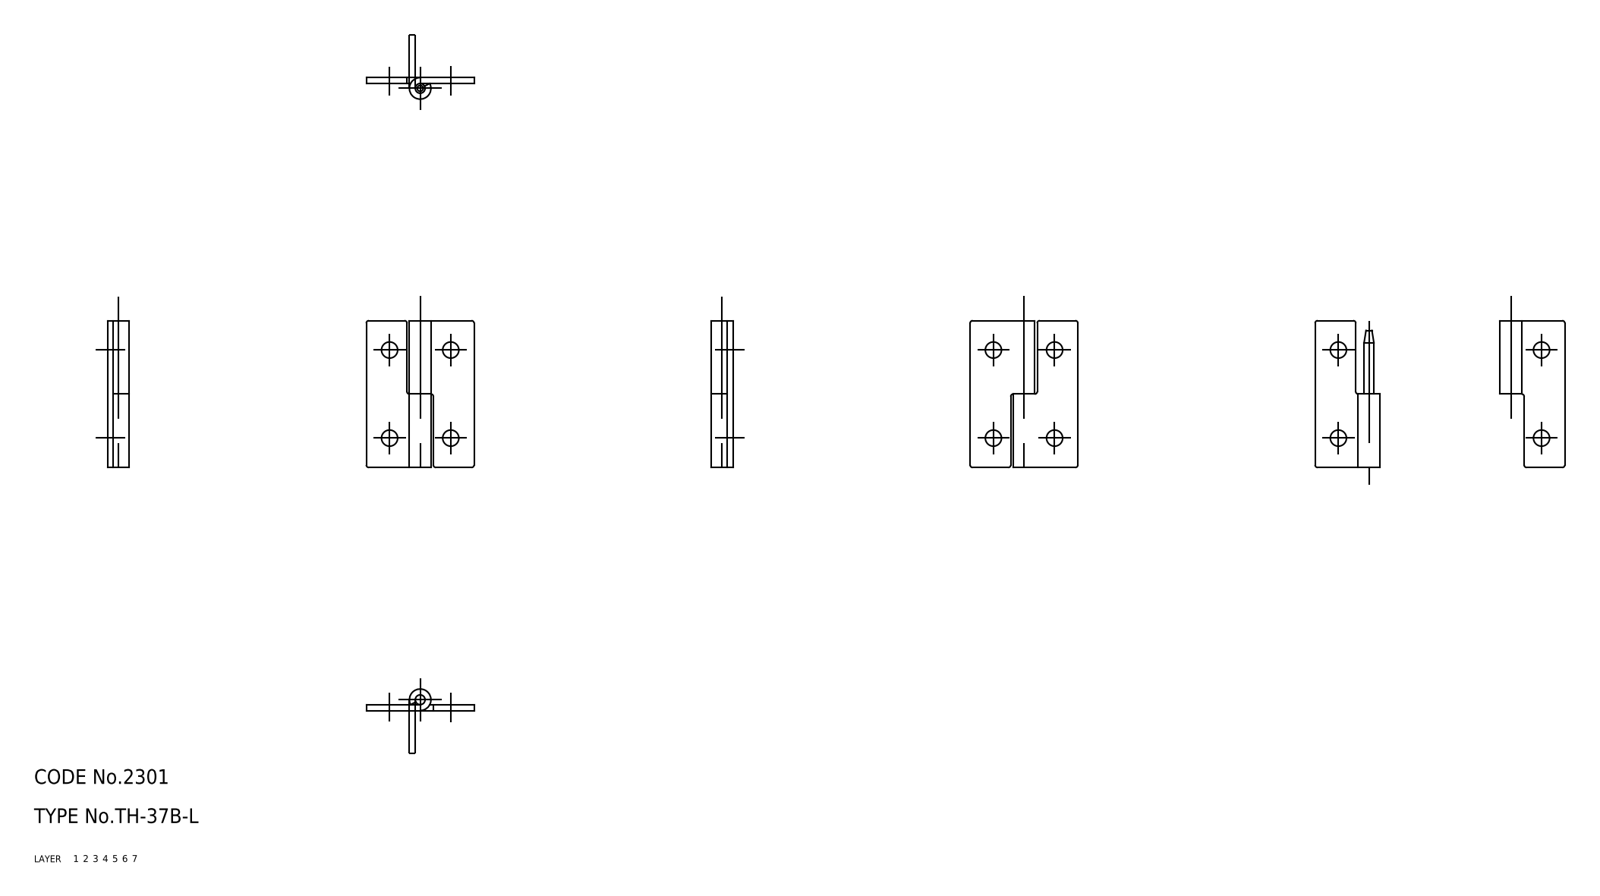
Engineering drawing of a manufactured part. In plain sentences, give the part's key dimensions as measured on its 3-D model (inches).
The part is named "shaft; hinge piece_B; hinge piece_A; TH_37B_L_8239_36". Its 3-D file was written by "CADfix (AUTOMOTIVE_DESIGN)". It is 3 solids with 42 faces: 0 planar, 0 cylindrical and 42 other. Overall it measures 1.181 by 0.866 by 0.173 inches. Its volume is 0.063 cubic inches and its surface area 3.171 square inches.
